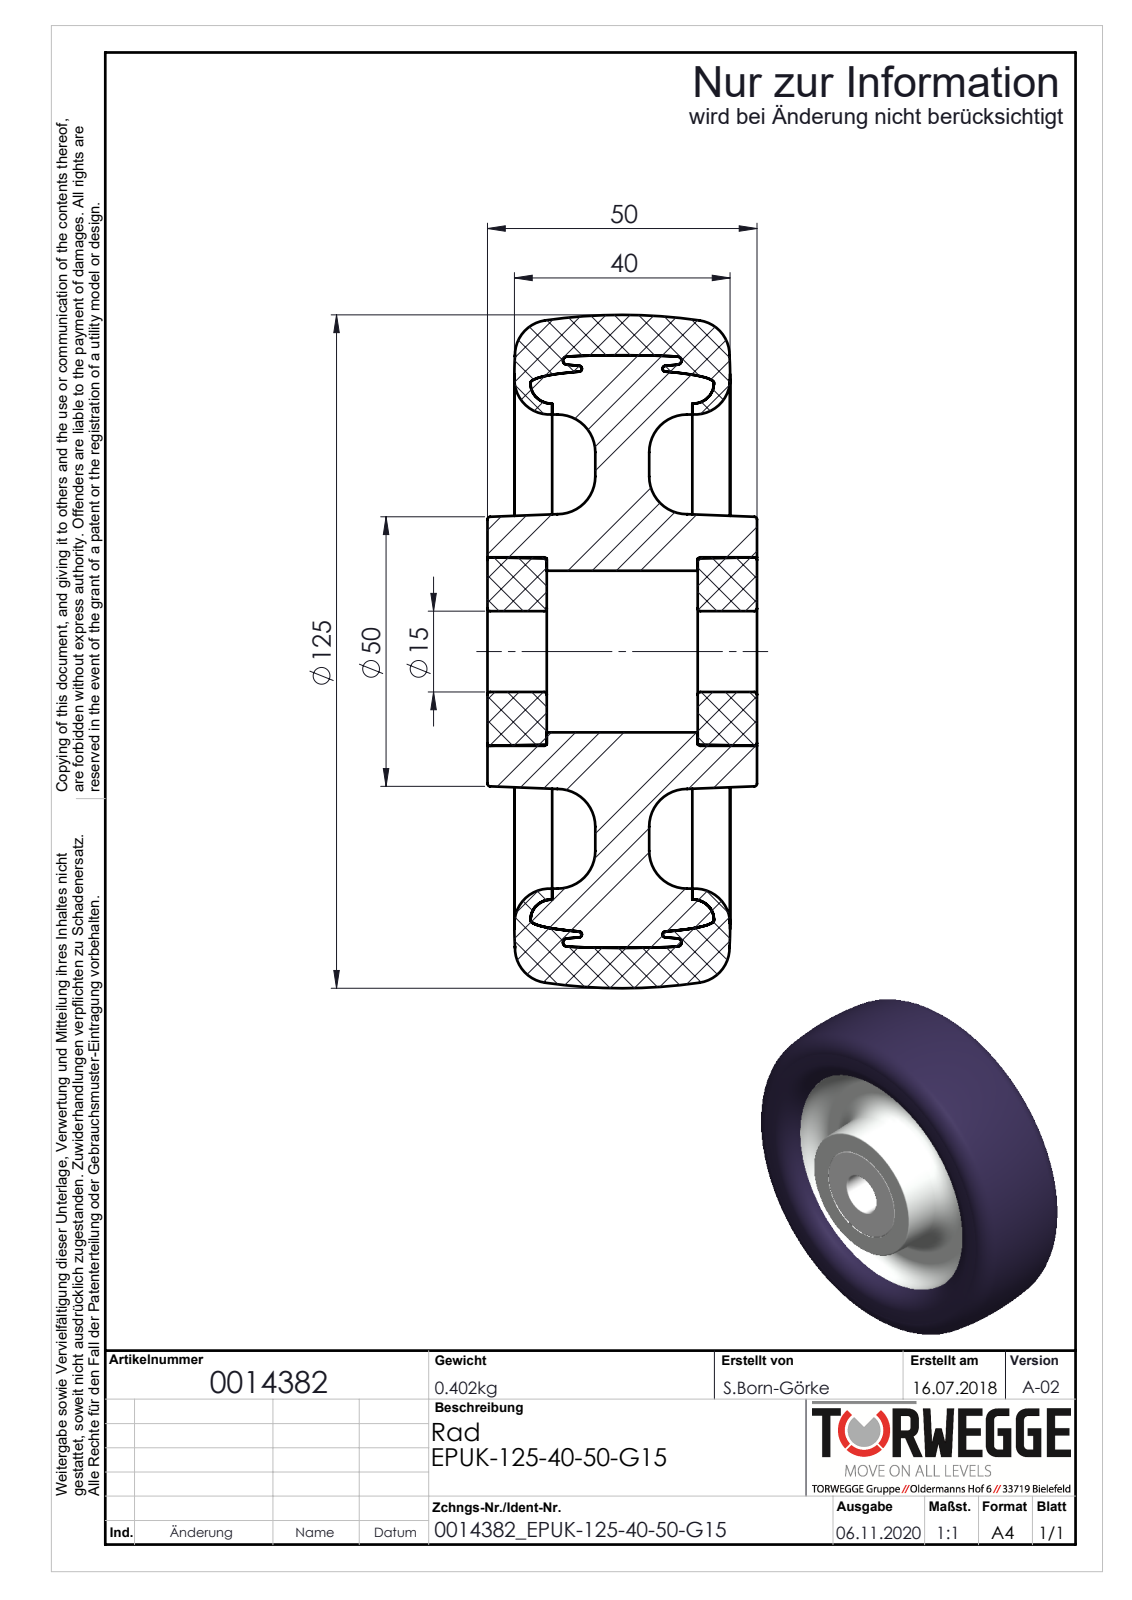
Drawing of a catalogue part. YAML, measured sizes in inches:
part_name: "0014382"
step_written_by: "SolidWorks 2018 (AUTOMOTIVE_DESIGN)"
units: inches
bodies: {solids: 3, faces: 192, planar: 44, cylindrical: 26, other: 122}
overall_size: [4.921, 4.921, 1.969]
volume: 21.62
surface_area: 90.52
round_holes:
  - {diameter: 0.591, count: 1}
  - {diameter: 1.181, count: 1}
  - {diameter: 3.465, count: 1}
round_bosses_or_shafts:
  - {diameter: 2.008, count: 1}
  - {diameter: 1.378, count: 1}
partial_cylinders:
  - {radius: 2.047, count: 1}
face_to_face_distances: [0.787, 1.181, 0.433, 1.535, 0.354, 0.748, 1.969, 0.394, 1.102, 0.472]
